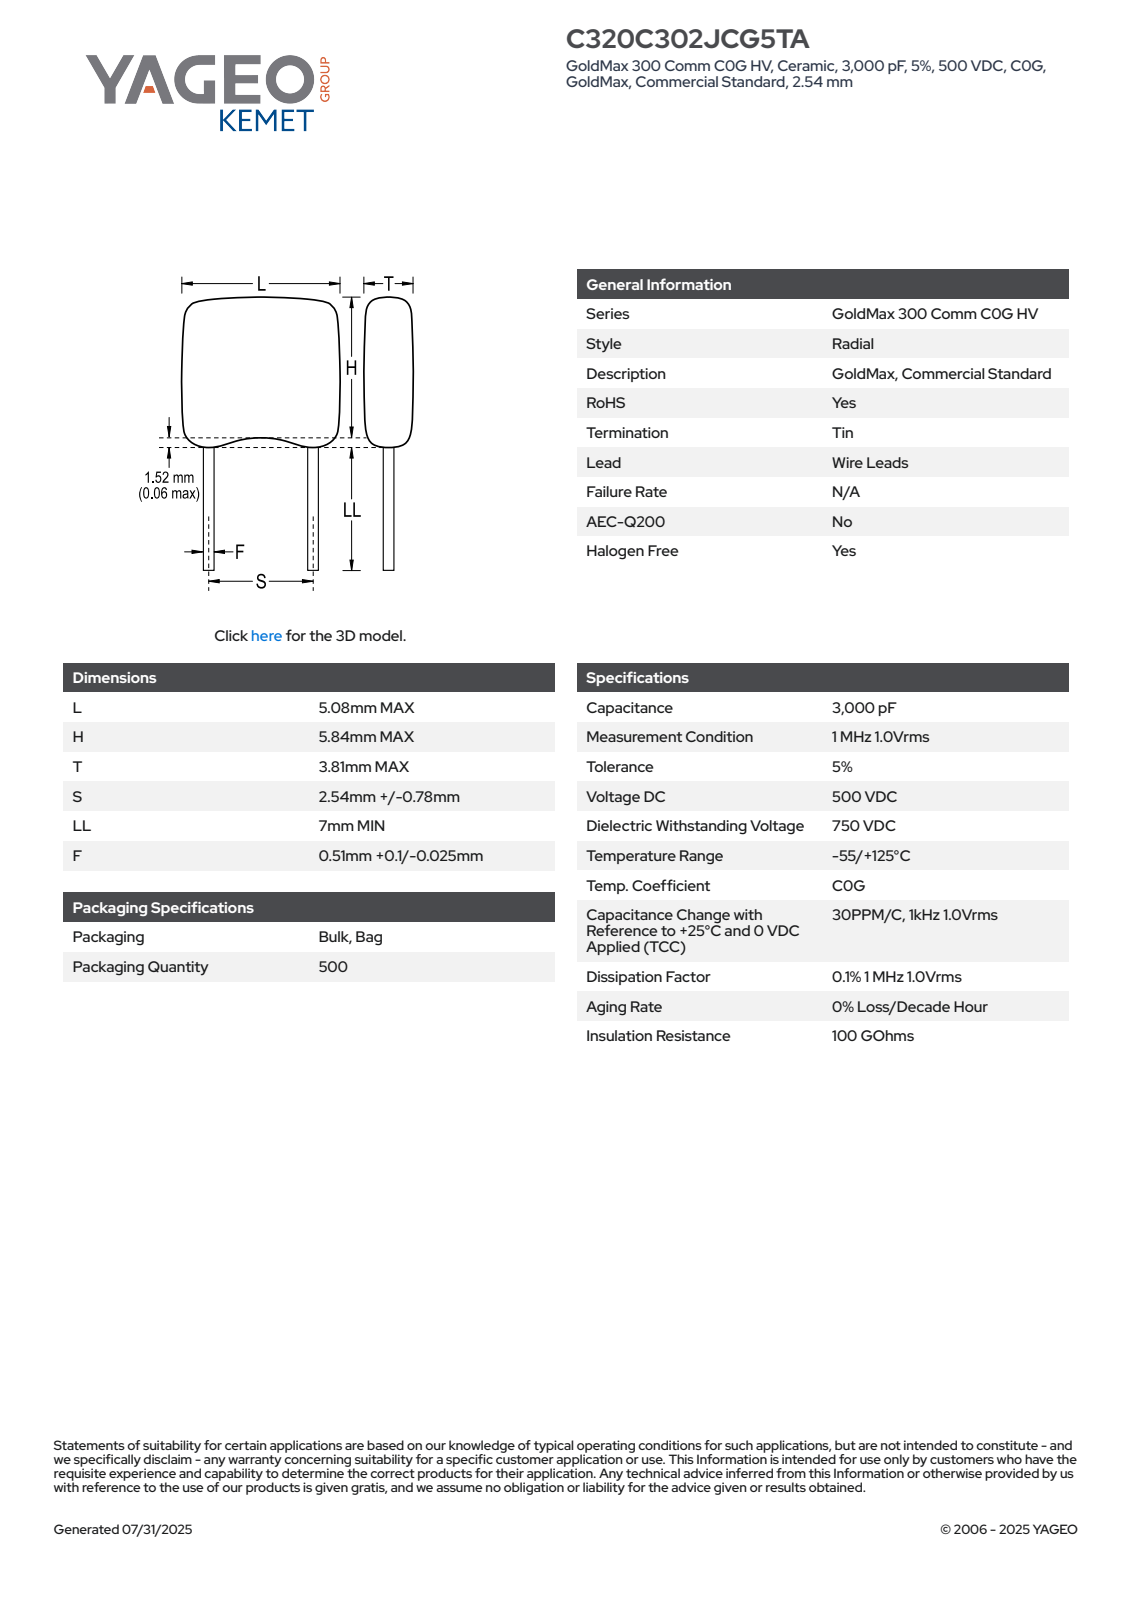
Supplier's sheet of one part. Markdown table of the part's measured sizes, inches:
| quantity | value |
| --- | --- |
| part name | CCR_KRCST_C320_L5.08H5.84T3.81S2.54LL7F0.61 |
| STEP written by | SolidWorks 2014 (AUTOMOTIVE_DESIGN) |
| units | inches |
| bodies | 4 solids, 83 faces (65 planar, 14 cylindrical, 4 other) |
| overall size | 0.565 × 0.2 × 0.15 |
| volume | 0.009 in³ |
| surface area | 0.277 in² |
| round bosses / shafts (diameter × count) | 0.024 × 2 |
| partial cylindrical surfaces (radius × count) | 0.03 × 10 |
| main face-to-face distances | 0.15, 0.2, 0.29, 0.276, 0.565, 0.021, 0.432, 0.157, 0.133, 0.411 |
